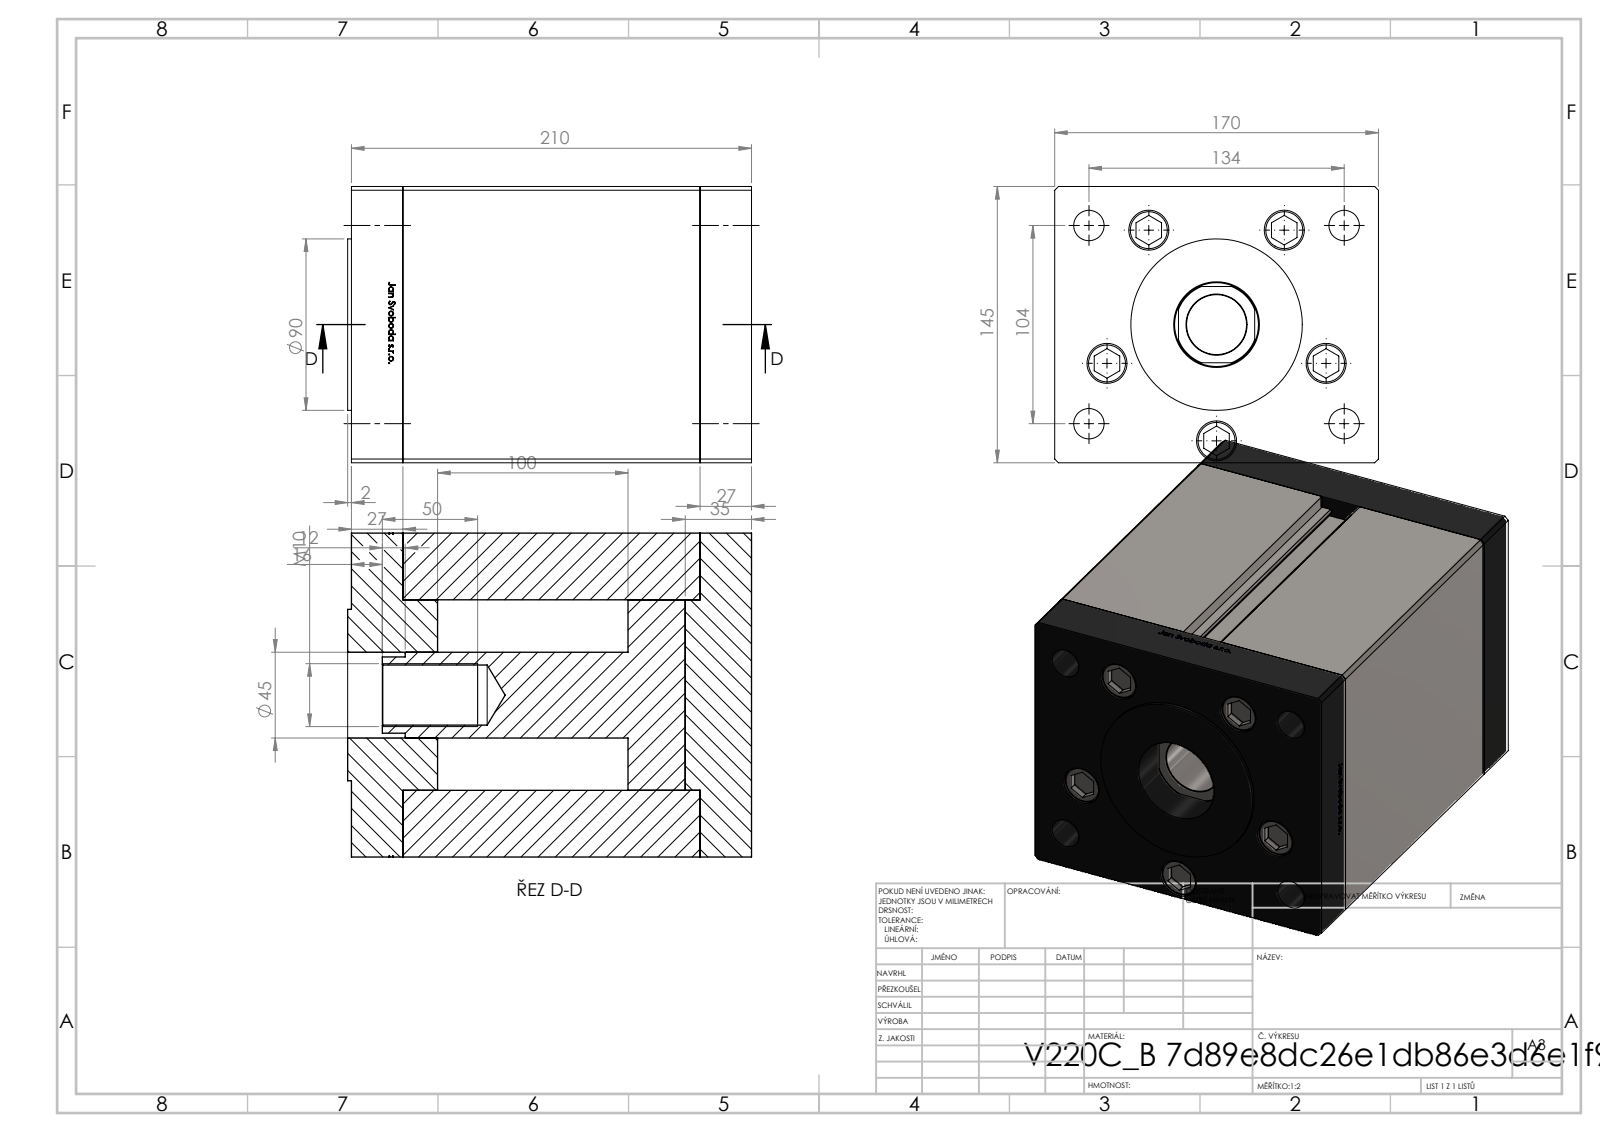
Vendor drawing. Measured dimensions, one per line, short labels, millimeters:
name: V220C BACK_B; V220C_VC_B; ALLEN BOLT; V220C_B MIDDLE (+1 more)
written by: SolidWorks 2019 (CONFIG_CONTROL_DESIGN)
unit: mm
bodies: 14 solids, 1185 faces (464 planar, 147 cylindrical, 574 other)
size: 231 × 170 × 145
volume: 4 515 000 mm³; area: 433 039 mm²
holes: 5× ⌀17.5, 5× ⌀21, 4× ⌀16, 2× ⌀2, 2× ⌀13.16, 1× ⌀31.5, 1× ⌀45
bosses: 5× ⌀8, 1× ⌀100, 1× ⌀90
rounds: 2× R0.93, 1× R22
face distances: 145, 27, 183, 156, 170, 38, 11, 210, 172, 174
hole spacings: 61, 84.81, 31.53, 33.06, 67.6, 70.44, 72.95, 73.26
